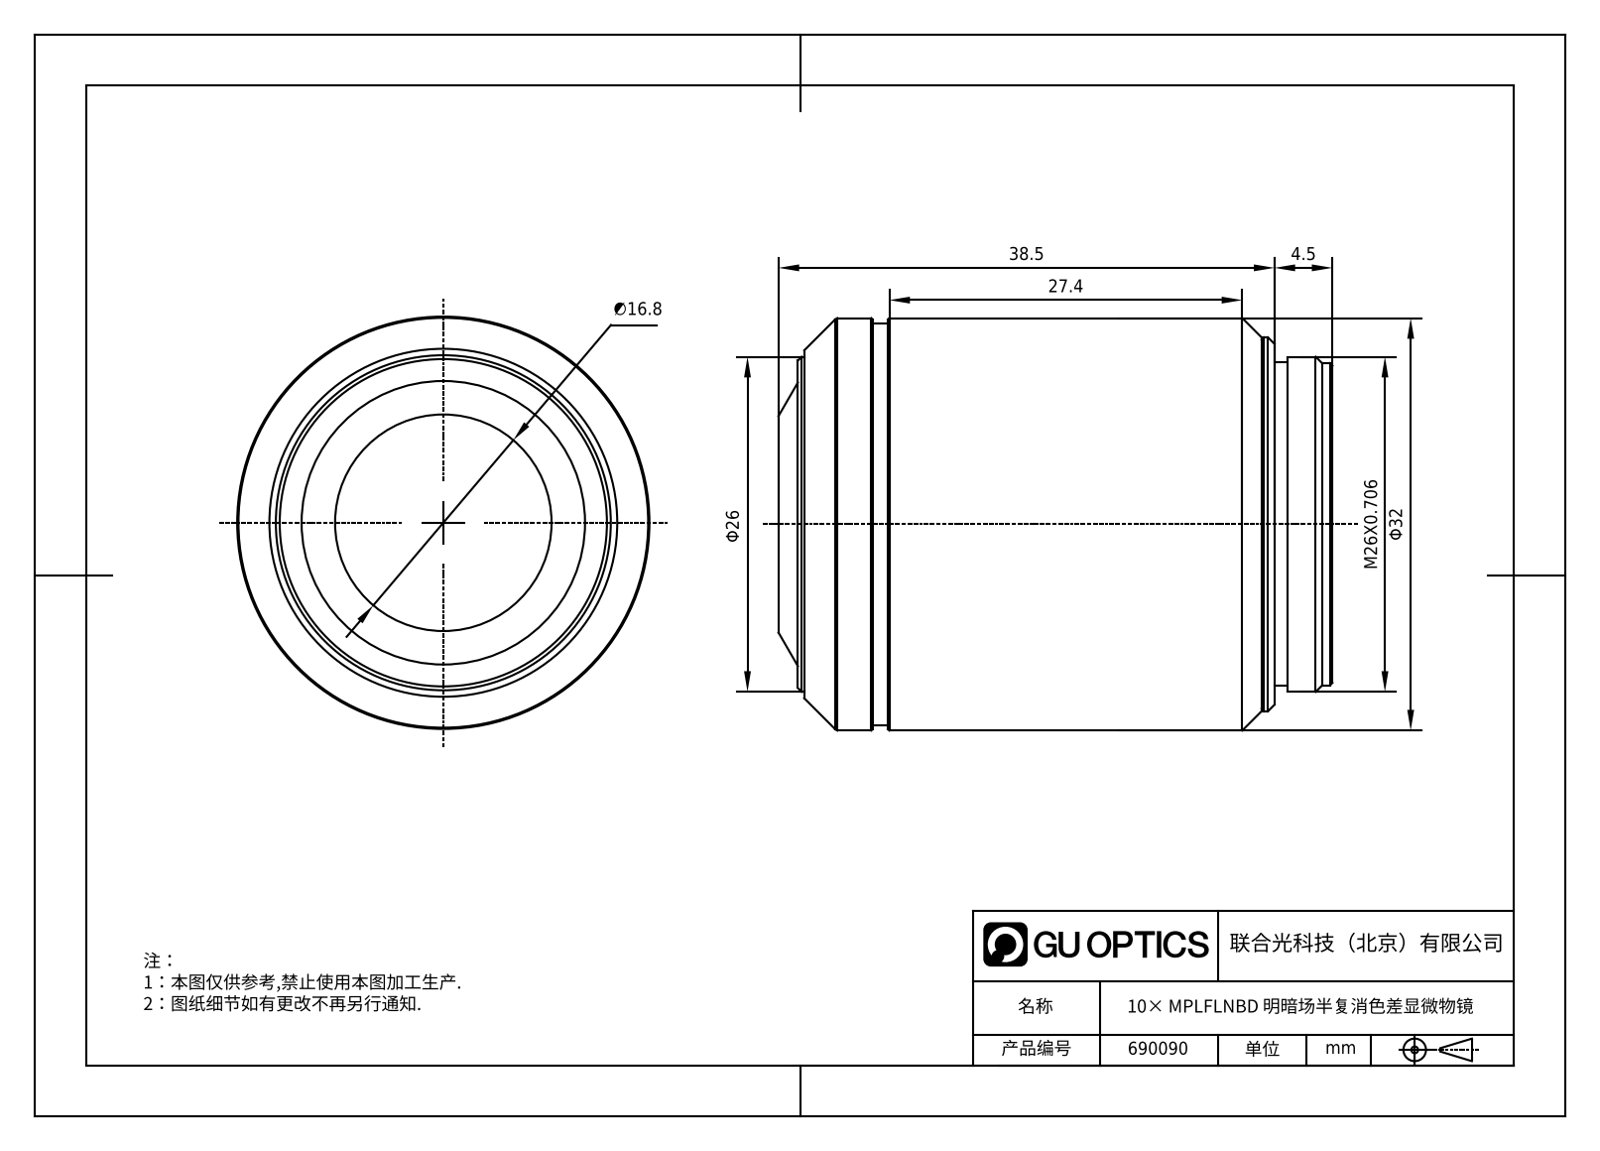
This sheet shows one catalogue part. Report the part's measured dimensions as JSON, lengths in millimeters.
{"part_name": "690090; 690090.stp; MPLFLN10XBD.stp", "step_written_by": "SolidWorks 2020 (CONFIG_CONTROL_DESIGN)", "units": "millimeters", "bodies": {"solids": 1, "faces": 47, "planar": 9, "cylindrical": 16, "other": 22}, "overall_size": [43, 32, 32], "volume_mm3": 31759, "surface_area_mm2": 5535, "round_bosses_or_shafts": [[32, 1], [31.2, 1], [29, 1], [26, 1], [25.1, 1], [25, 1]], "face_to_face_distances": [43, 1.5, 41.5, 38.5, 37, 4.5, 2, 37.5, 1, 0.5]}
